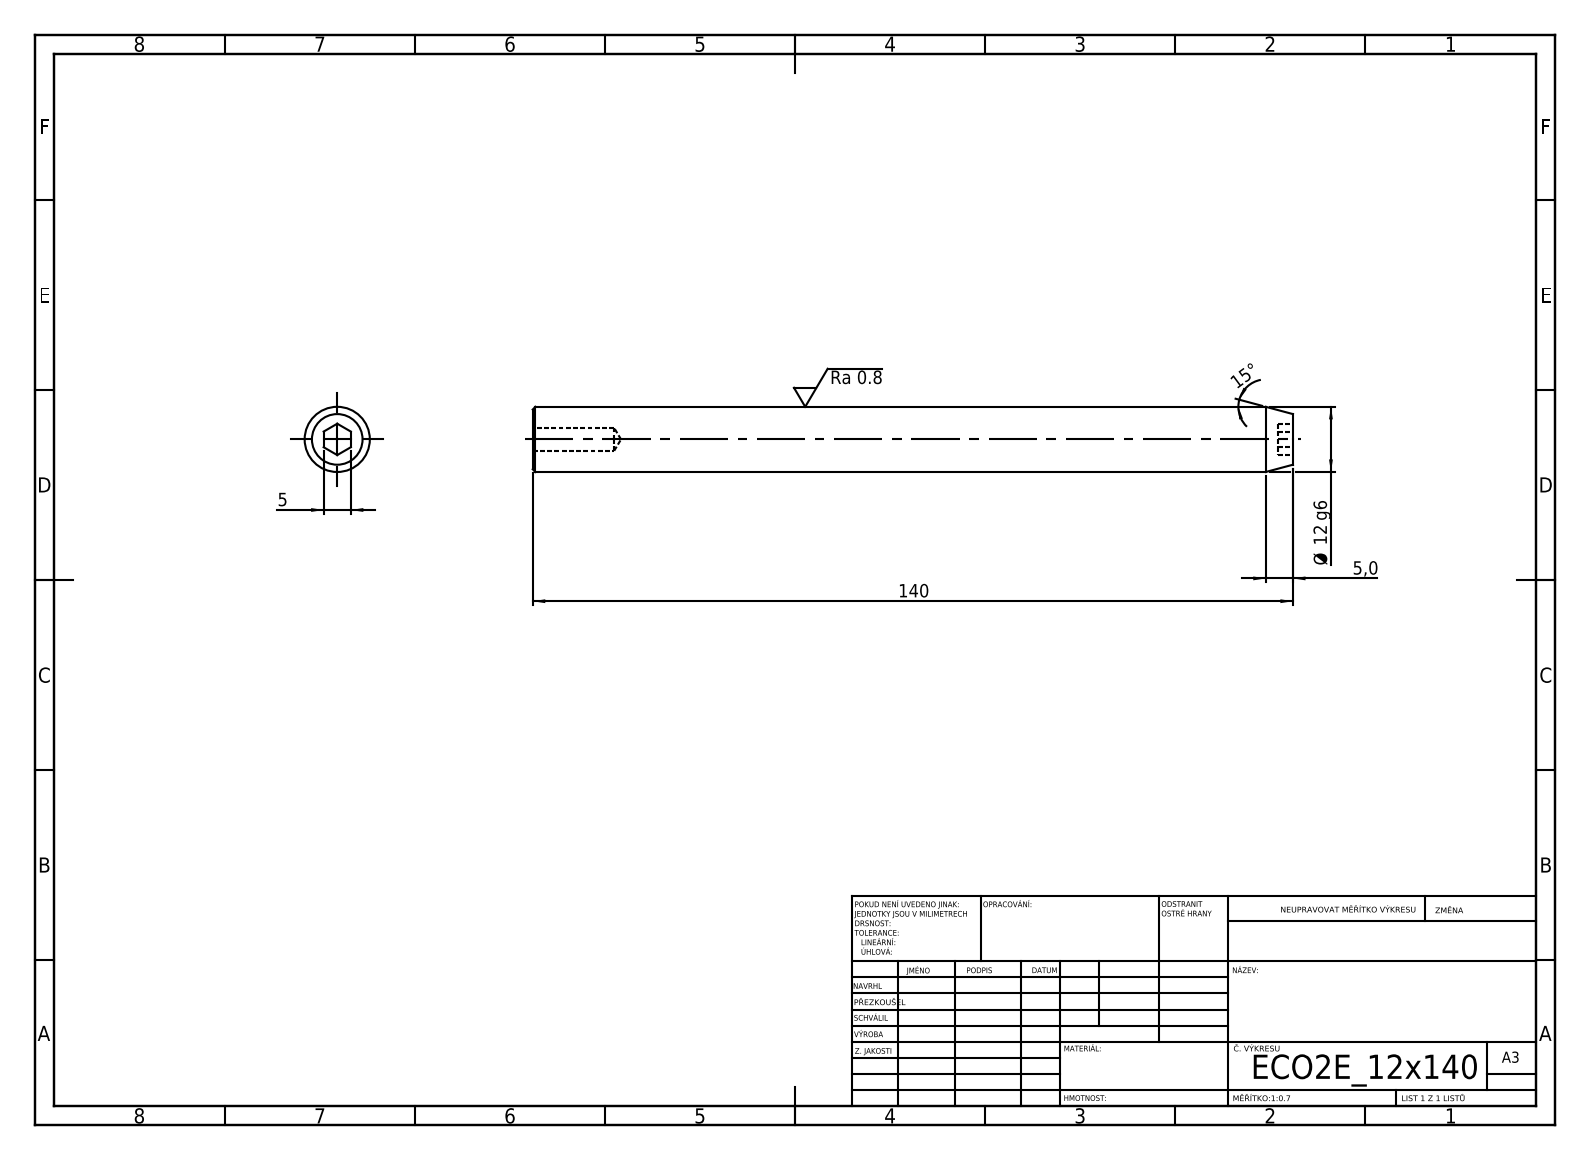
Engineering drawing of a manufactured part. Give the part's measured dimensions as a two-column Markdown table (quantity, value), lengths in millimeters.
| quantity | value |
| --- | --- |
| STEP written by | SolidWorks 2019 (CONFIG_CONTROL_DESIGN) |
| units | millimeters |
| bodies | 1 solid, 19 faces (9 planar, 4 cylindrical, 6 other) |
| overall size | 140 × 12 × 12 |
| volume | 15 438 mm³ |
| surface area | 5 681 mm² |
| round holes (diameter × count) | 4.2 × 1 |
| round bosses / shafts (diameter × count) | 12 × 1 |
| main face-to-face distances | 140, 5, 2.8, 137.2 |
